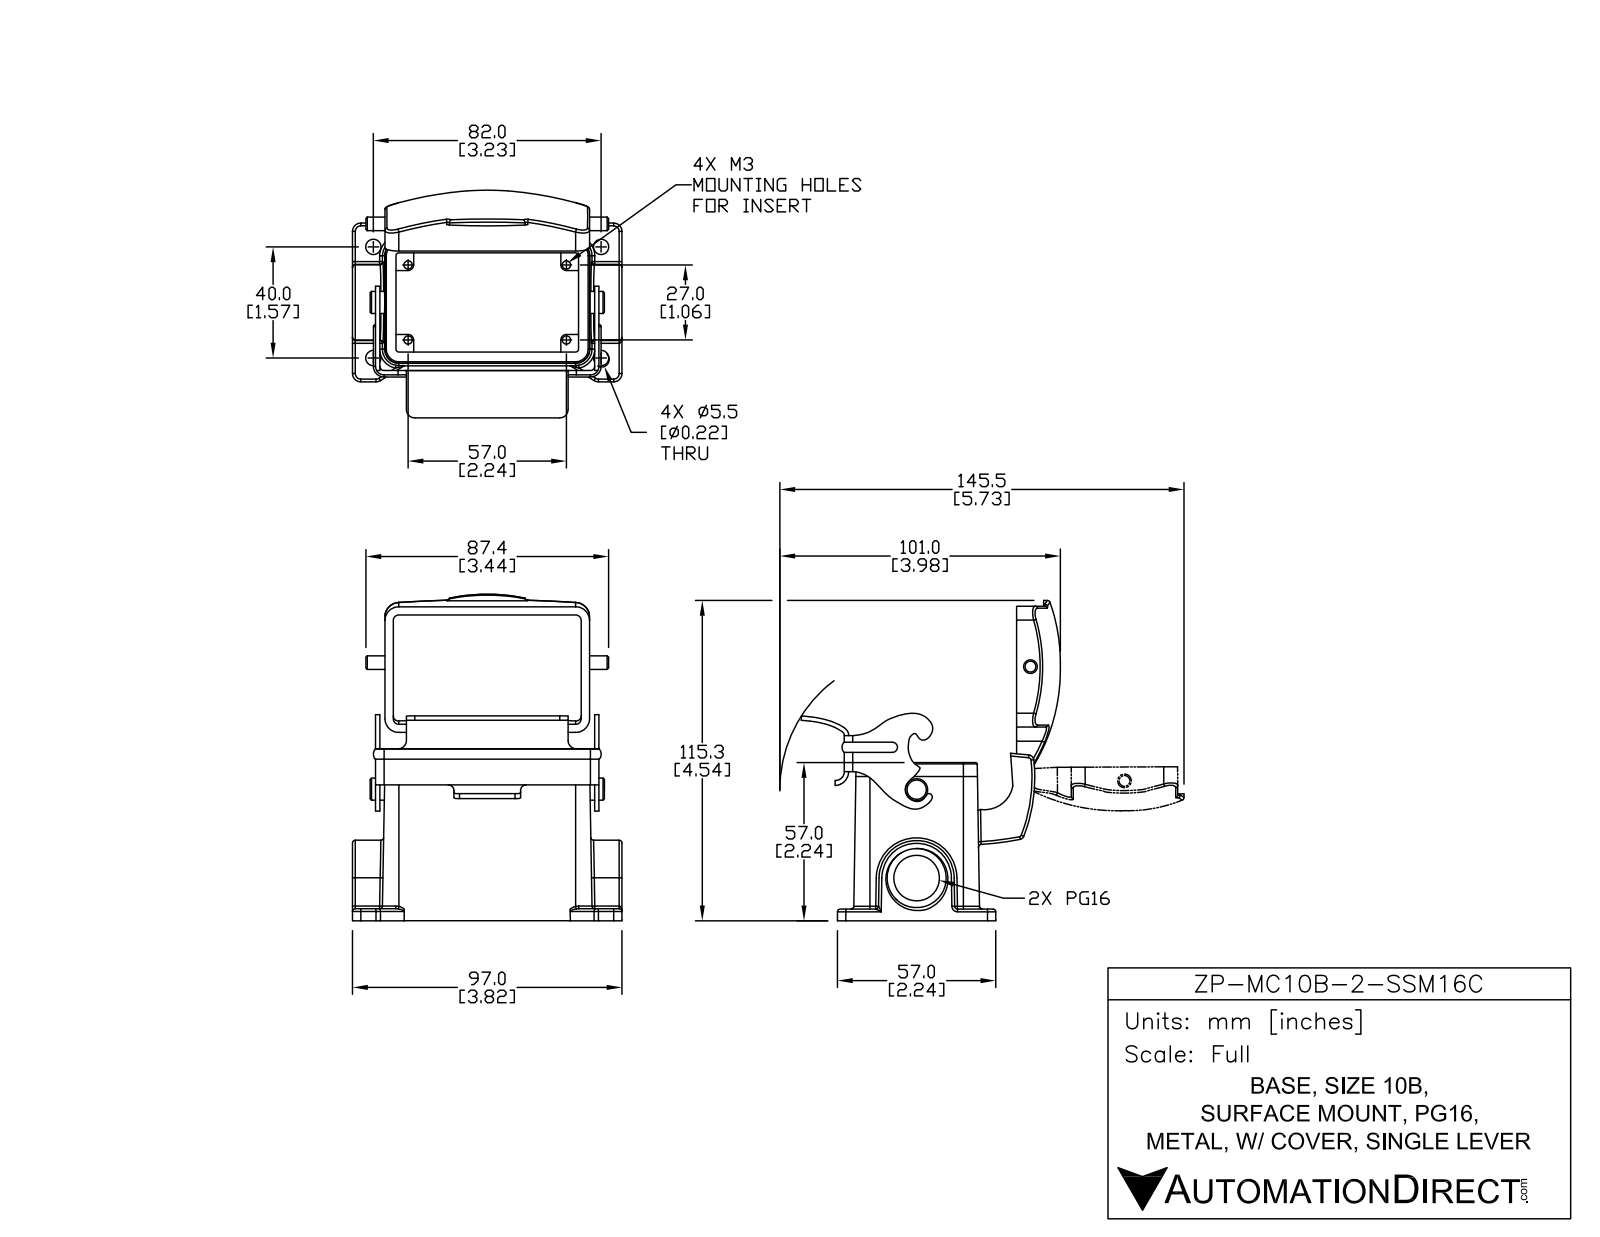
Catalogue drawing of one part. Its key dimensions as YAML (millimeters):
part_name: "ZP-MC10B-2-SSM16C"
step_written_by: "SolidWorks 2014 (AUTOMOTIVE_DESIGN)"
units: millimeters
bodies: {solids: 3, faces: 370, planar: 137, cylindrical: 124, other: 109}
overall_size: [114.77, 97, 81.94]
volume: 103865
surface_area: 57814
round_holes:
  - {diameter: 3, count: 4}
  - {diameter: 5.5, count: 4}
  - {diameter: 16.4, count: 1}
  - {diameter: 21.25, count: 1}
round_bosses_or_shafts:
  - {diameter: 7.95, count: 1}
  - {diameter: 4.9, count: 1}
partial_cylinders:
  - {radius: 1, count: 27}
  - {radius: 2, count: 14}
  - {radius: 3, count: 12}
  - {radius: 5, count: 6}
  - {radius: 0.5, count: 4}
  - {radius: 1.5, count: 2}
  - {radius: 3.06, count: 2}
  - {radius: 8, count: 2}
face_to_face_distances: [3.95, 3.96, 1.56, 4.03, 3, 78.86, 40.49, 13.71, 66.71, 12.15]
hole_center_spacings: [14.09, 35.76, 69.8, 77.15, 27, 40, 57, 63.07]
